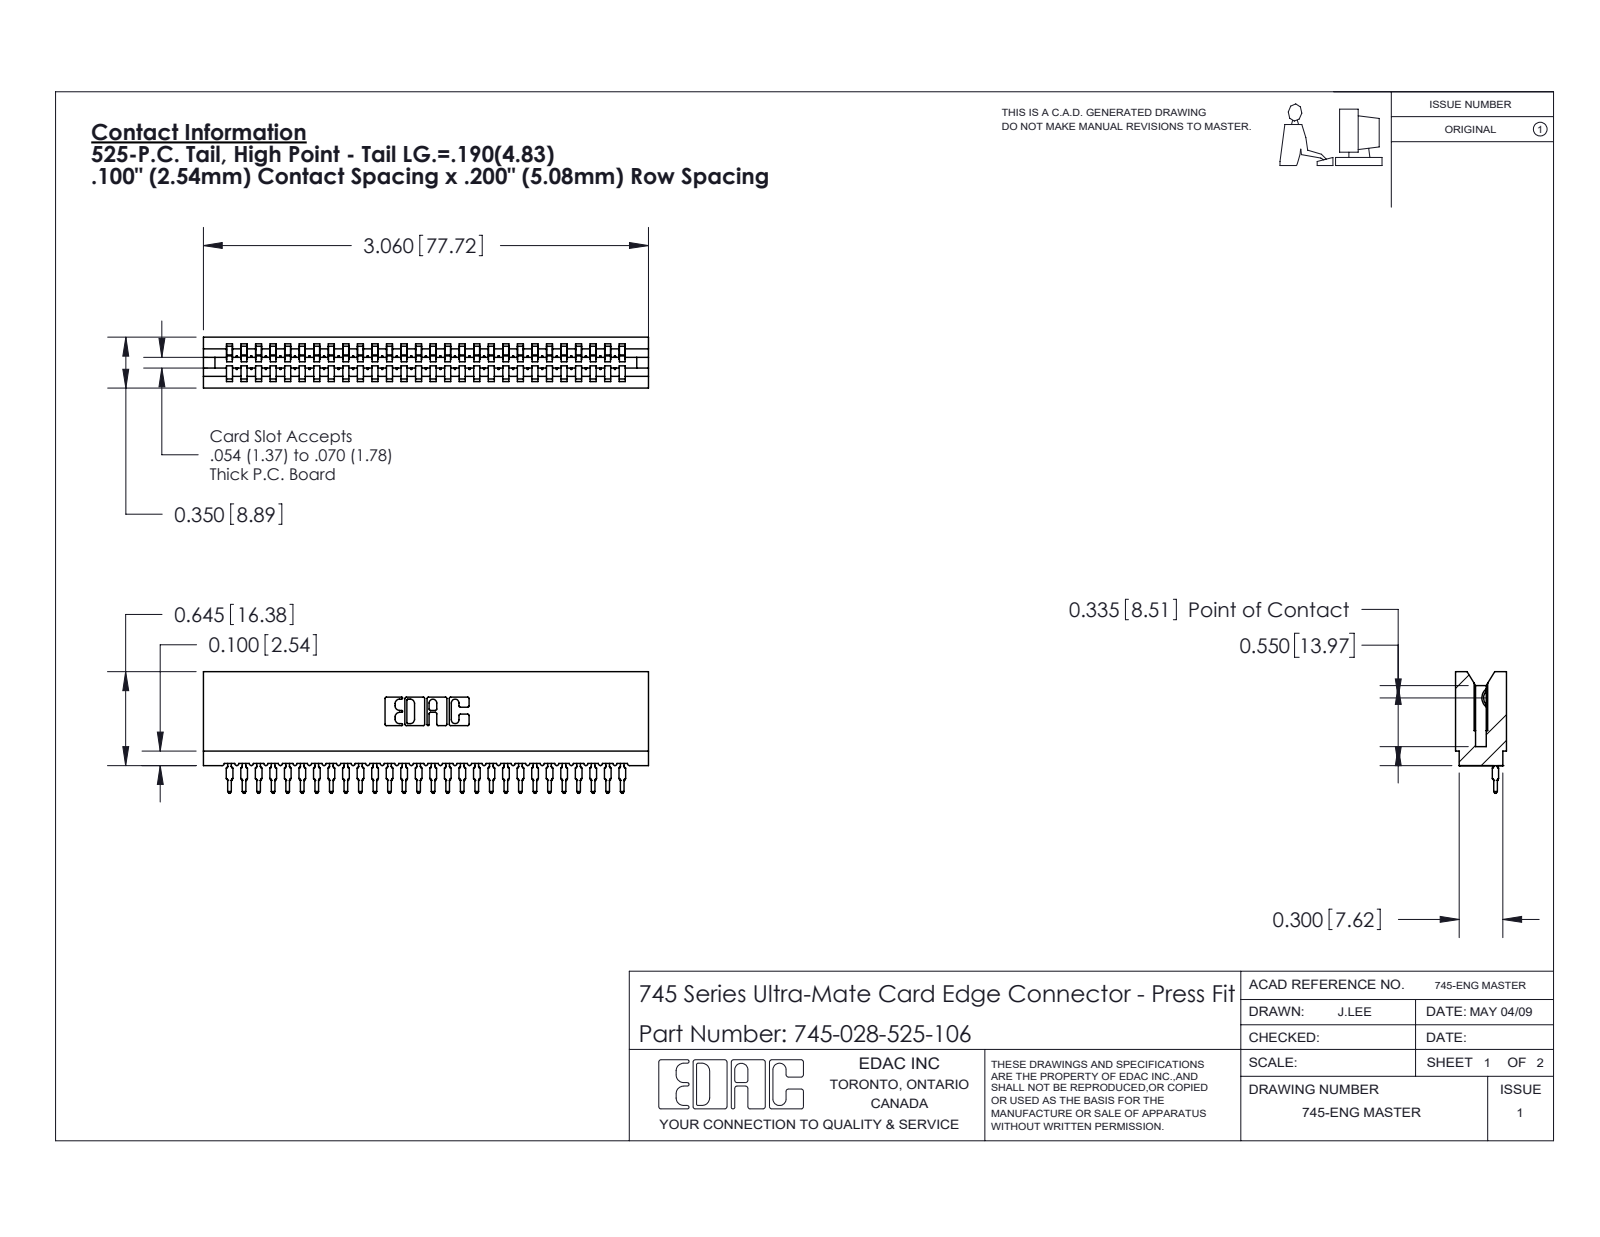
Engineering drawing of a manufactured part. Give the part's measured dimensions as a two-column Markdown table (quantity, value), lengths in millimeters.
| quantity | value |
| --- | --- |
| part name | 745-292-001_525; 745-028-525-106; 745 Part_Insulator Option - 06 |
| STEP written by | SolidWorks 2020 (CONFIG_CONTROL_DESIGN) |
| units | millimeters |
| bodies | 29 solids, 3232 faces (1932 planar, 572 cylindrical, 728 other) |
| overall size | 77.7 × 21.2 × 8.9 |
| volume | 6 780 mm³ |
| surface area | 12 320 mm² |
| partial cylindrical surfaces (radius × count) | 0.4 × 56, 0.5 × 56, 0.3 × 22, 0.2 × 6, 0.8 × 6, 0.1 × 4, 0.3 × 4, 0.7 × 3 |
| main face-to-face distances | 2.5, 8.9, 5.1, 3.5, 5.4, 1.1, 7.7, 2.4, 4.2, 7.6 |
